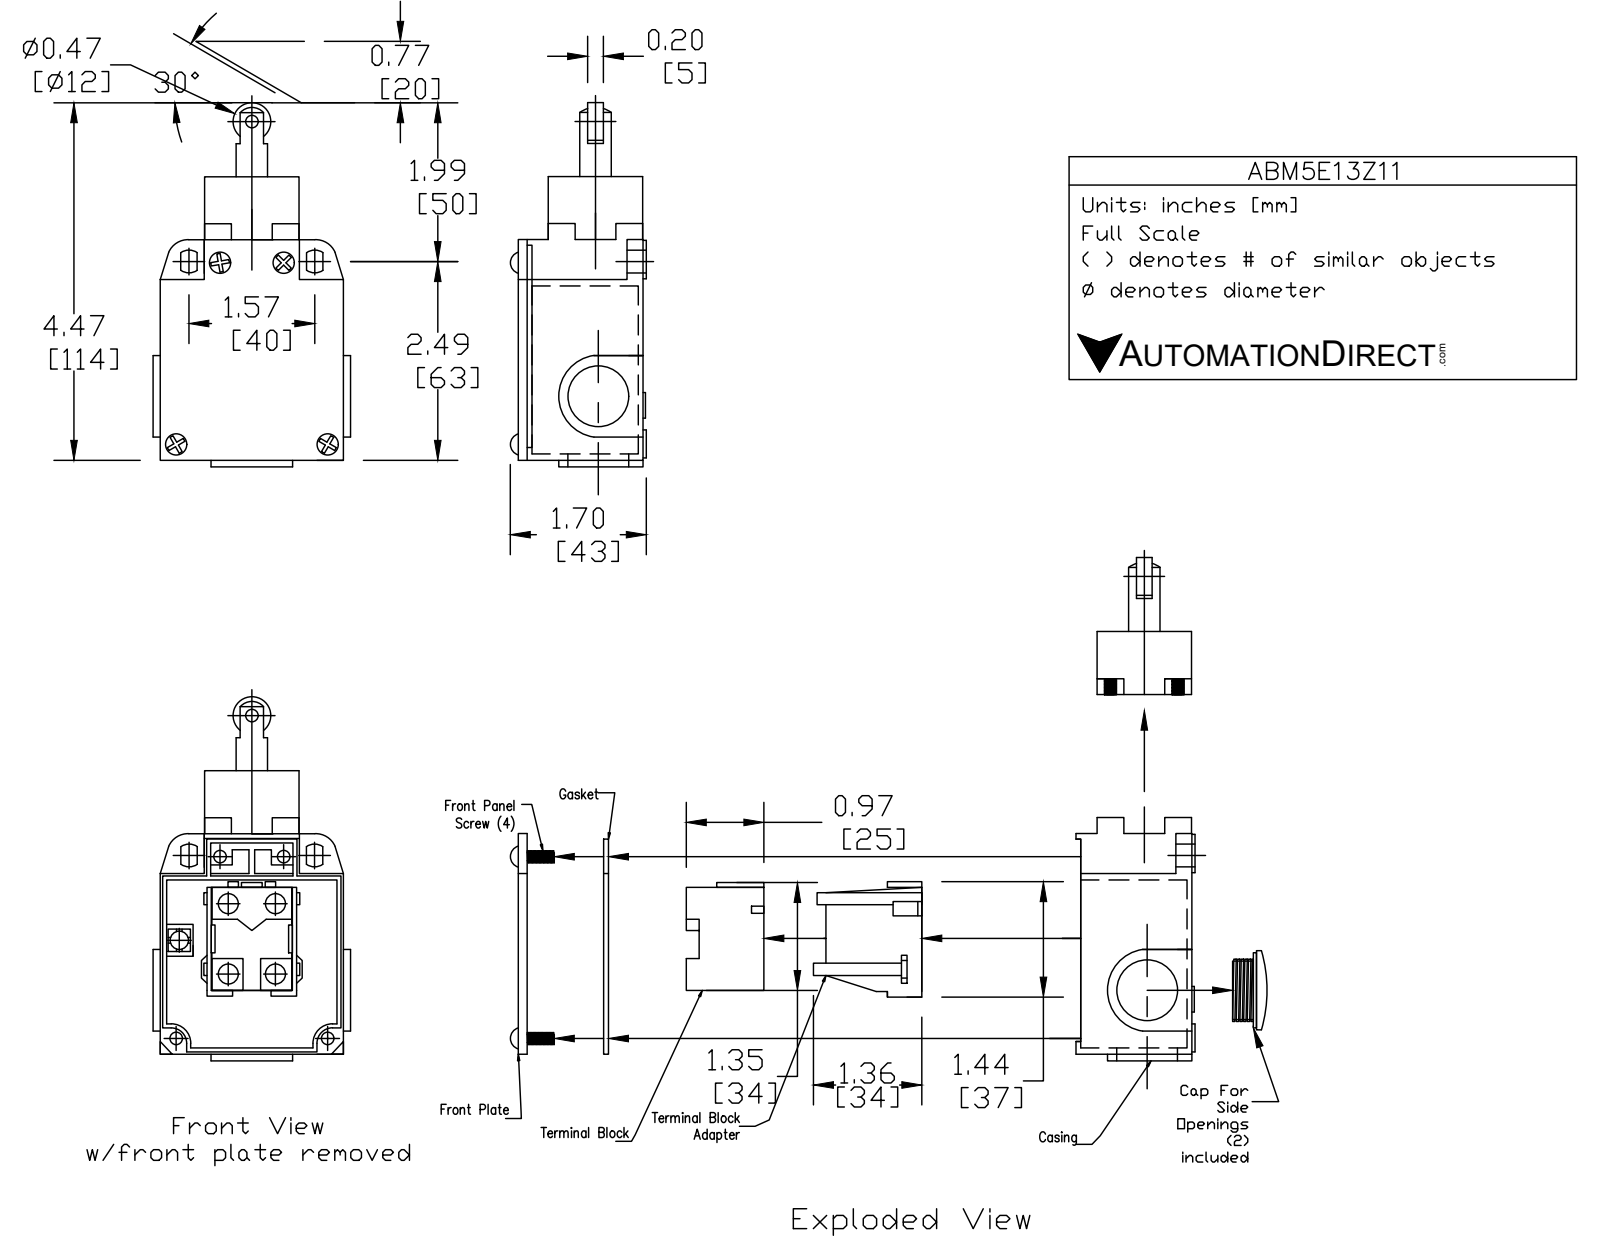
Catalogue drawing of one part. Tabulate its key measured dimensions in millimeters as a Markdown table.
| quantity | value |
| --- | --- |
| part name | ABM5E13Z11 |
| STEP written by | SolidWorks 2017 (AUTOMOTIVE_DESIGN) |
| units | millimeters |
| bodies | 4 solids, 167 faces (77 planar, 68 cylindrical, 22 other) |
| overall size | 119.9 × 43.3 × 40 |
| volume | 128 500 mm³ |
| surface area | 25 080 mm² |
| round holes (diameter × count) | 5.2 × 2, 10 × 1, 17 × 1, 19 × 1 |
| round bosses / shafts (diameter × count) | 10 × 4, 7 × 2, 12 × 1 |
| partial cylindrical surfaces (radius × count) | 1.5 × 16, 1 × 4, 5 × 4, 3.3 × 2, 11.5 × 1, 12 × 1 |
| main face-to-face distances | 40, 39.5, 30, 5, 35, 9.5, 76.5, 81.5, 15, 77 |
| hole center spacings | 1, 67.1 |
